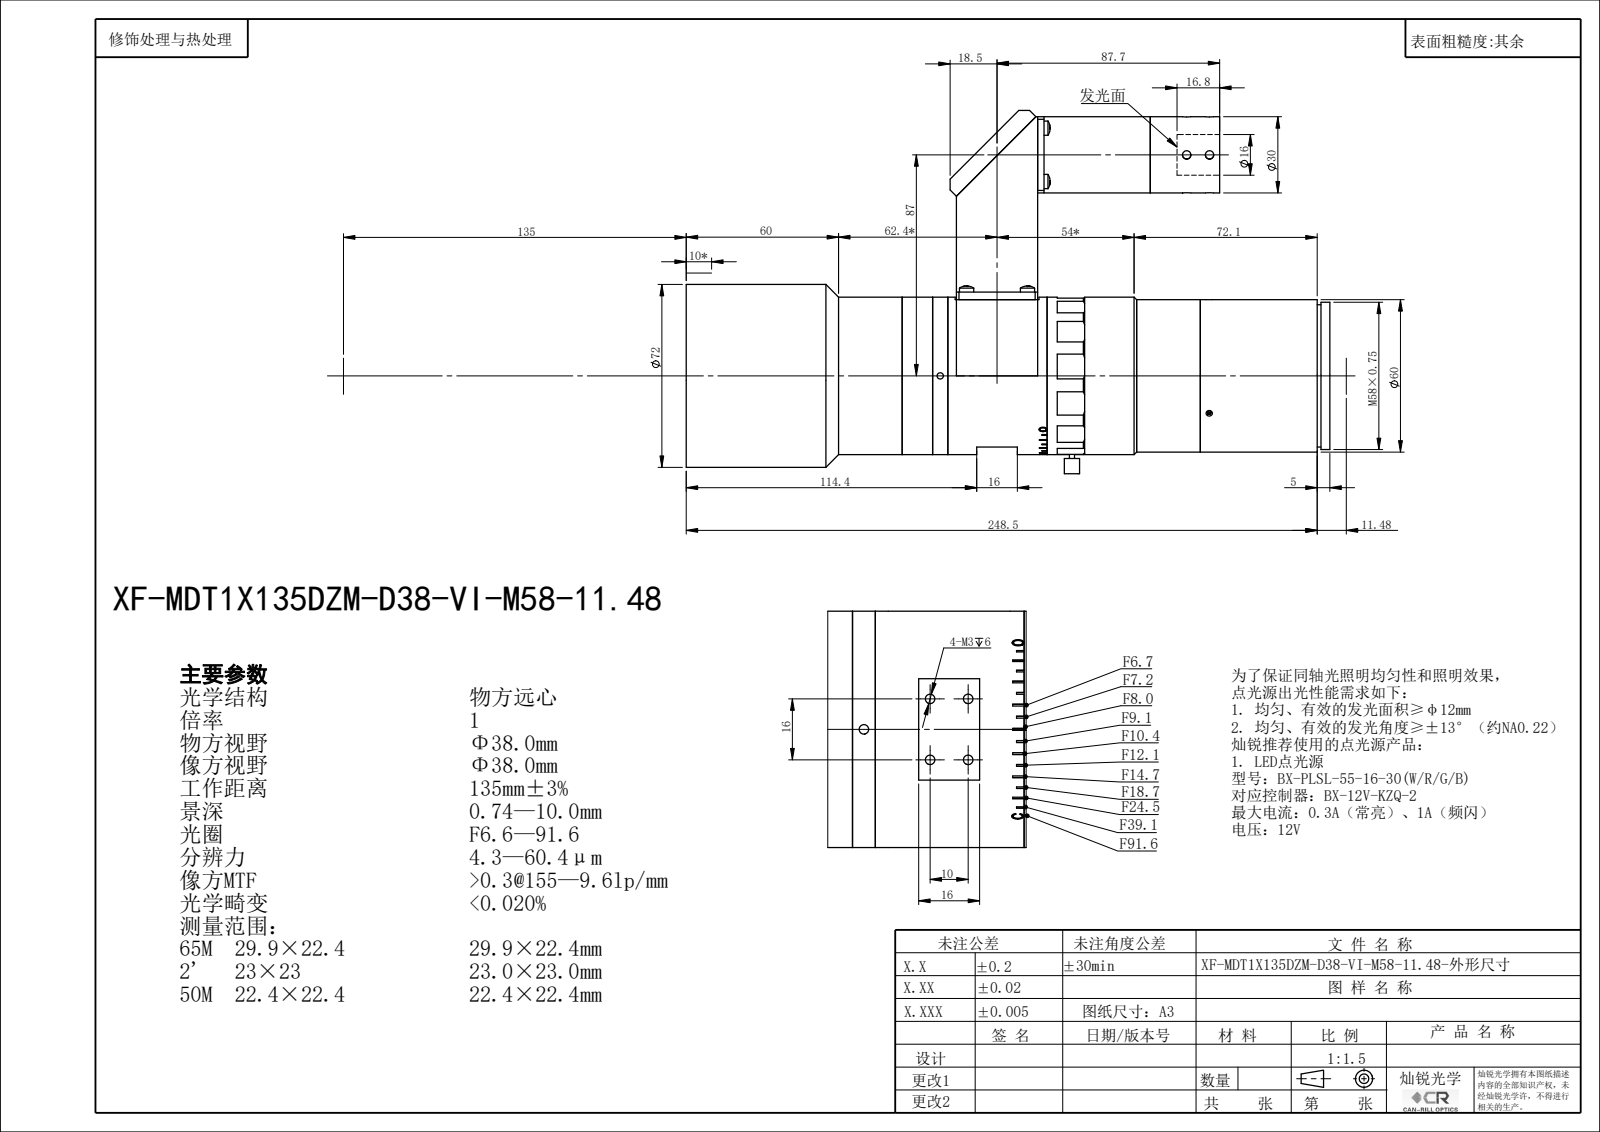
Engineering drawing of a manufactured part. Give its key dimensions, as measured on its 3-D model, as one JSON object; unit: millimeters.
{"part_name": "XF-MDT1X135DZM-D38-VI-M58-11.48", "step_written_by": "SolidWorks 2022 (CONFIG_CONTROL_DESIGN)", "units": "millimeters", "bodies": {"solids": 0, "faces": 368, "planar": 183, "cylindrical": 130, "other": 55}, "overall_size": [253.52, 142.97, 72], "round_holes": [[2.5, 7], [3.3, 4], [16, 1], [36, 1], [40, 1], [46, 1], [64, 1], [66, 1]], "round_bosses_or_shafts": [[5.6, 8], [3.8, 4], [72, 1], [62, 1], [60, 1], [58, 1], [56, 1], [30, 1]], "partial_cylinders_radius": [[20, 13], [30.9, 1]], "face_to_face_distances": [42, 32, 10, 52, 96.07, 64.07, 35.7, 3.7, 60.37, 50.5], "hole_center_spacings": [9, 10, 16, 18.87, 87]}
